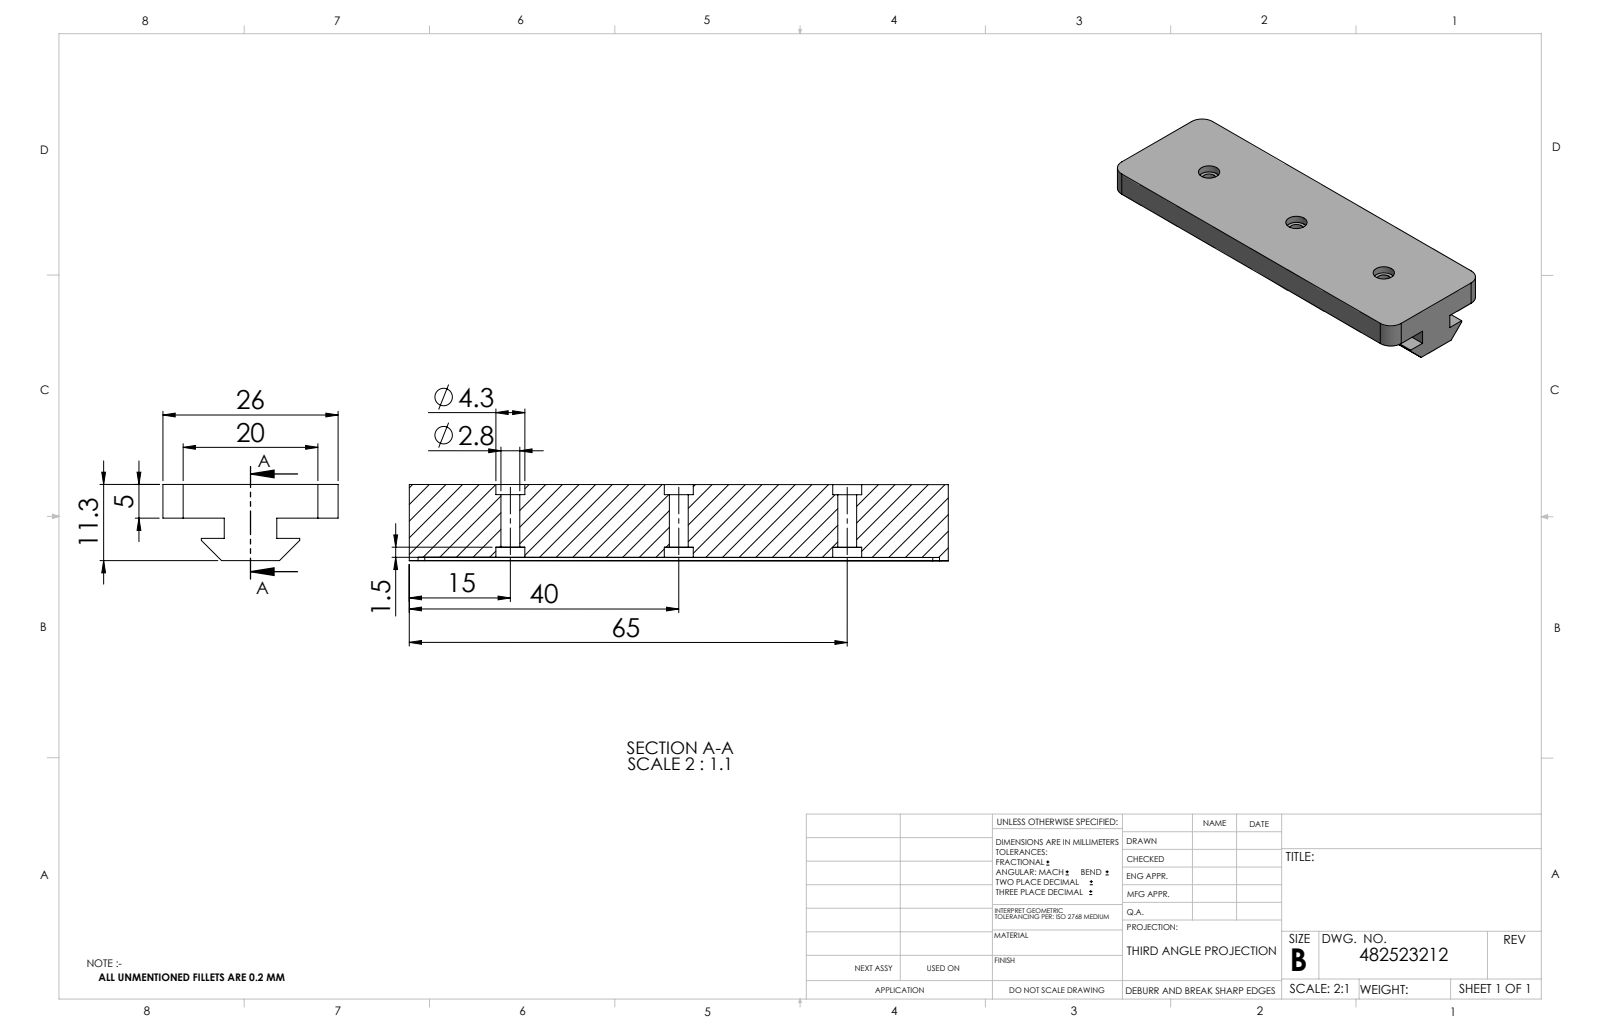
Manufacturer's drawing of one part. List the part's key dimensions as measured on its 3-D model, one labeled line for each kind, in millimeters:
Part name (STEP PRODUCT): 482523212_c_1
STEP written by: SolidWorks 2014 (CONFIG_CONTROL_DESIGN)
Units: millimetres
Bodies: 1 solid, 53 faces (27 planar, 26 cylindrical, 0 other)
Overall size (bounding box): 80 × 26 × 11.3
Volume: 14 853 mm³ · Surface area: 7 492 mm²
Round holes (diameter × count): ⌀2.8 ×3, ⌀4.3 ×3
Partial cylindrical surfaces — rounded edges, fillets, slot ends (radius × count): R1 ×4, R3 ×4
Main face-to-face distances: 5, 3, 8, 9.1, 16.9, 2.8, 5.8, 10.8, 26, 7.8
Hole centre spacings: 25, 50
